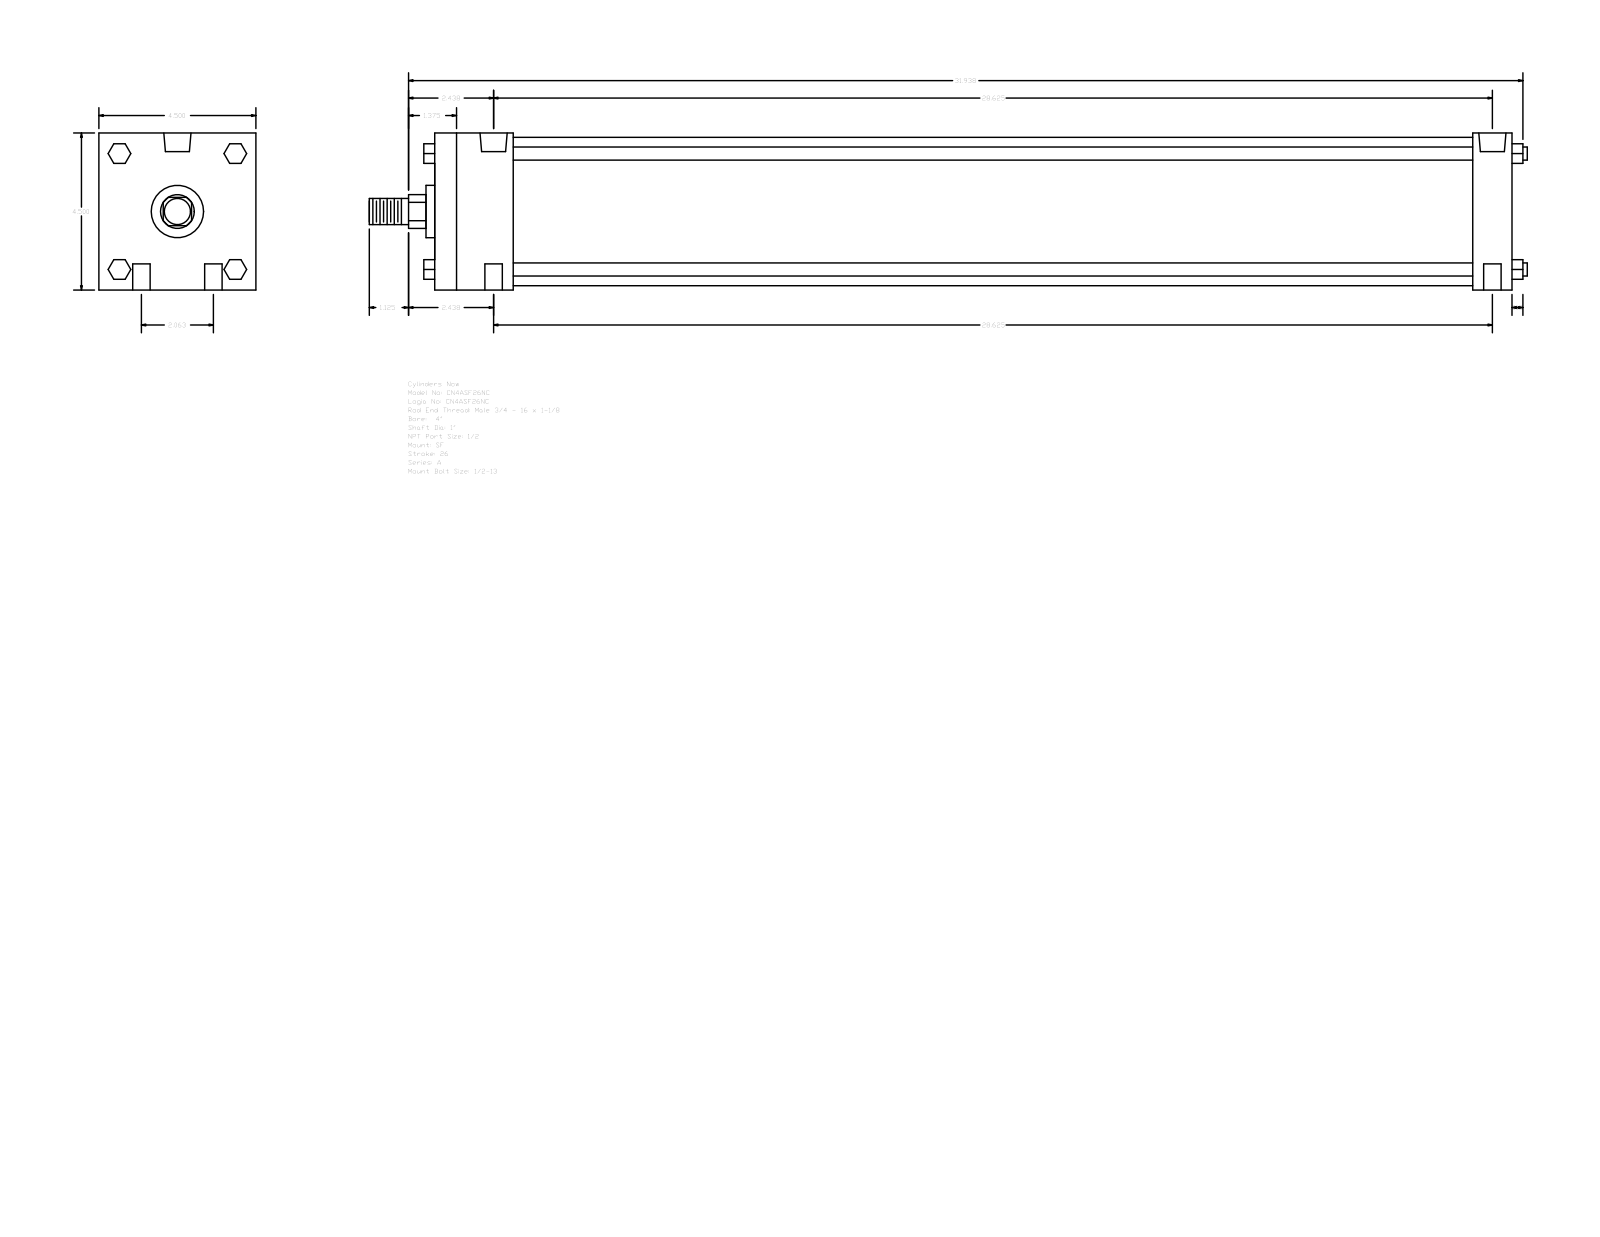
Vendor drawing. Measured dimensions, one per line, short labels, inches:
name: A_SF__0400_1
written by: GSSL Pune (CONFIG_CONTROL_DESIGN)
unit: in
bodies: 0 solids, 124 faces (94 planar, 30 cylindrical, 0 other)
size: 33.187 × 4.5 × 4.5
holes: 4× ⌀0.5, 2× ⌀0.344, 2× ⌀0.778
bosses: 4× ⌀0.375, 1× ⌀4.25, 1× ⌀1.5, 1× ⌀1, 1× ⌀0.75
rounds: 1× R0.484
face distances: 4.5, 30.875, 1.125, 29.75, 2.25, 27.5, 28.625, 0.563, 1.66, 2.875
hole spacings: 1.031, 28.644, 28.625, 2.062, 28.699, 28.375
